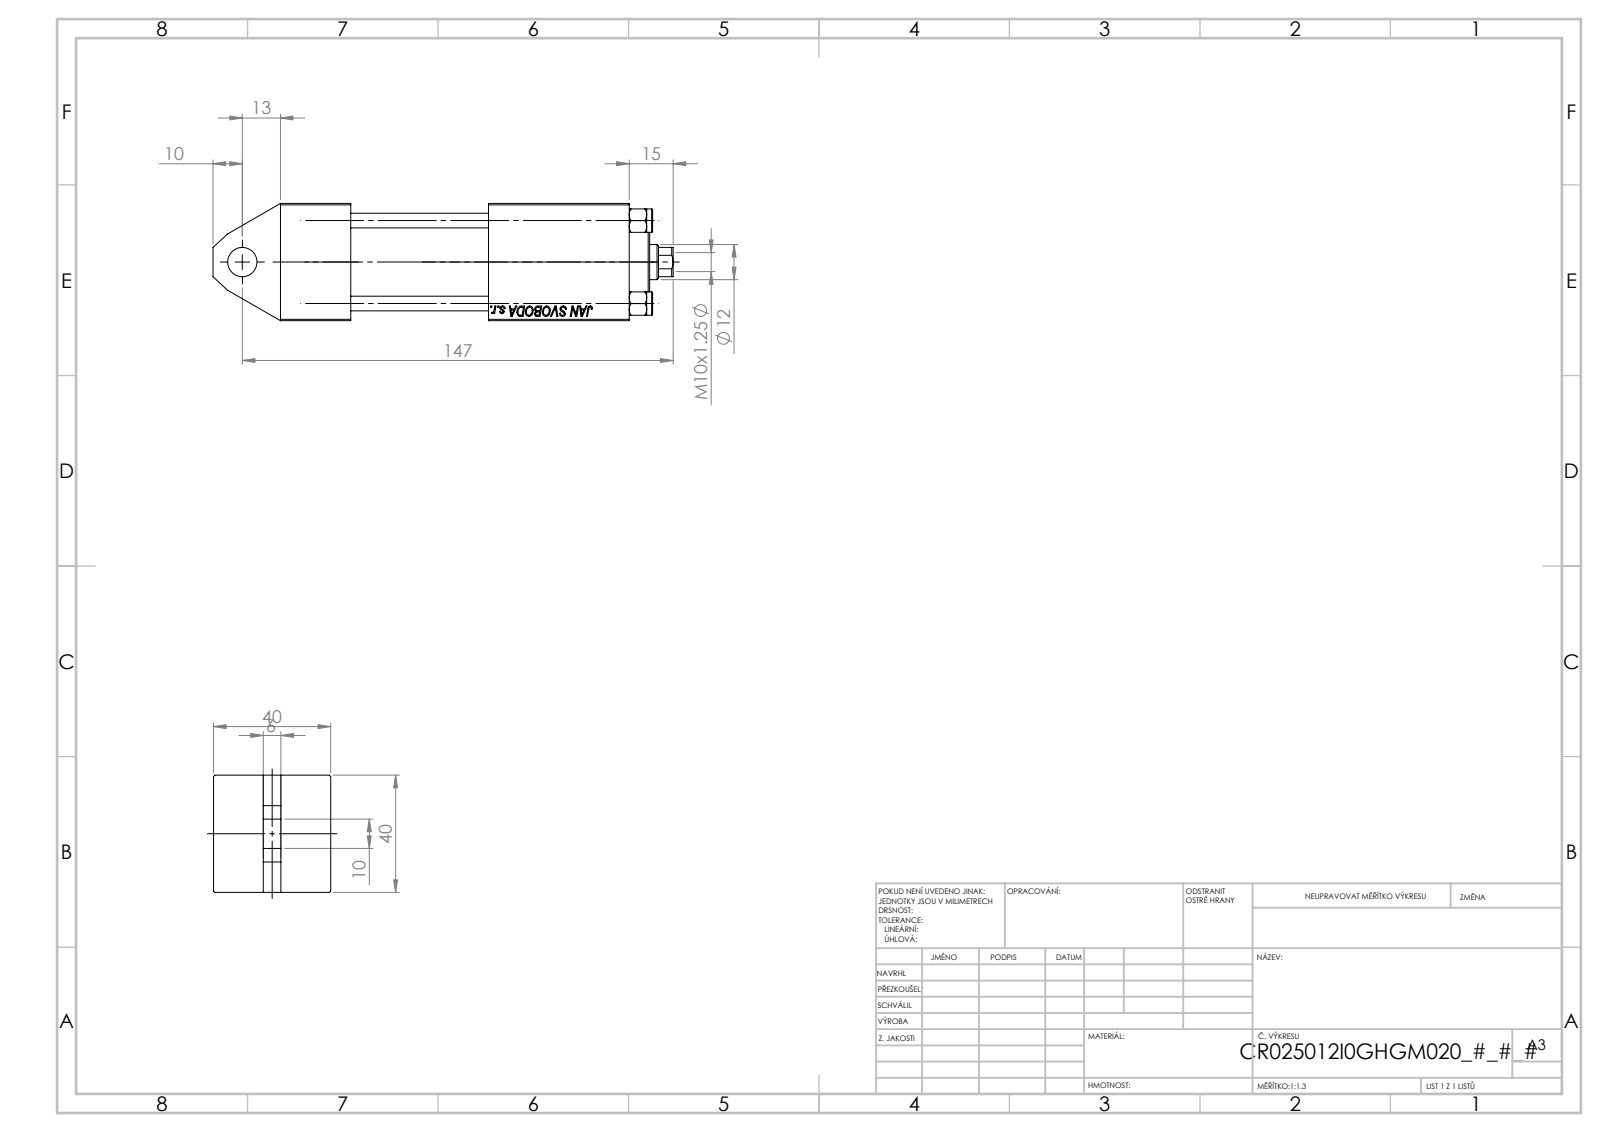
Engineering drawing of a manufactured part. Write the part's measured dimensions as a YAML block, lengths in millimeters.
part_name: "NUT_M5_I; V215CR_I_Body; V215CR_VCP_I; V215CR_TYCINKA_I (+1 more)"
step_written_by: "SolidWorks 2019 (CONFIG_CONTROL_DESIGN)"
units: millimeters
bodies: {solids: 11, faces: 1078, planar: 501, cylindrical: 81, other: 496}
overall_size: [157, 40, 40]
volume: 146453
surface_area: 57999
round_holes:
  - {diameter: 5, count: 4}
  - {diameter: 20, count: 3}
  - {diameter: 7, count: 2}
  - {diameter: 13.16, count: 2}
  - {diameter: 6.5, count: 1}
  - {diameter: 10, count: 1}
  - {diameter: 12, count: 1}
  - {diameter: 15, count: 1}
  - {diameter: 25, count: 1}
  - {diameter: 30, count: 1}
round_bosses_or_shafts:
  - {diameter: 8, count: 4}
  - {diameter: 31, count: 1}
  - {diameter: 24, count: 1}
partial_cylinders:
  - {radius: 5.5, count: 1}
face_to_face_distances: [40, 24, 23, 17, 119, 95, 47, 90.3, 66.3, 28.7]
hole_center_spacings: [20.01, 28.3, 40.02, 25, 72, 97]
